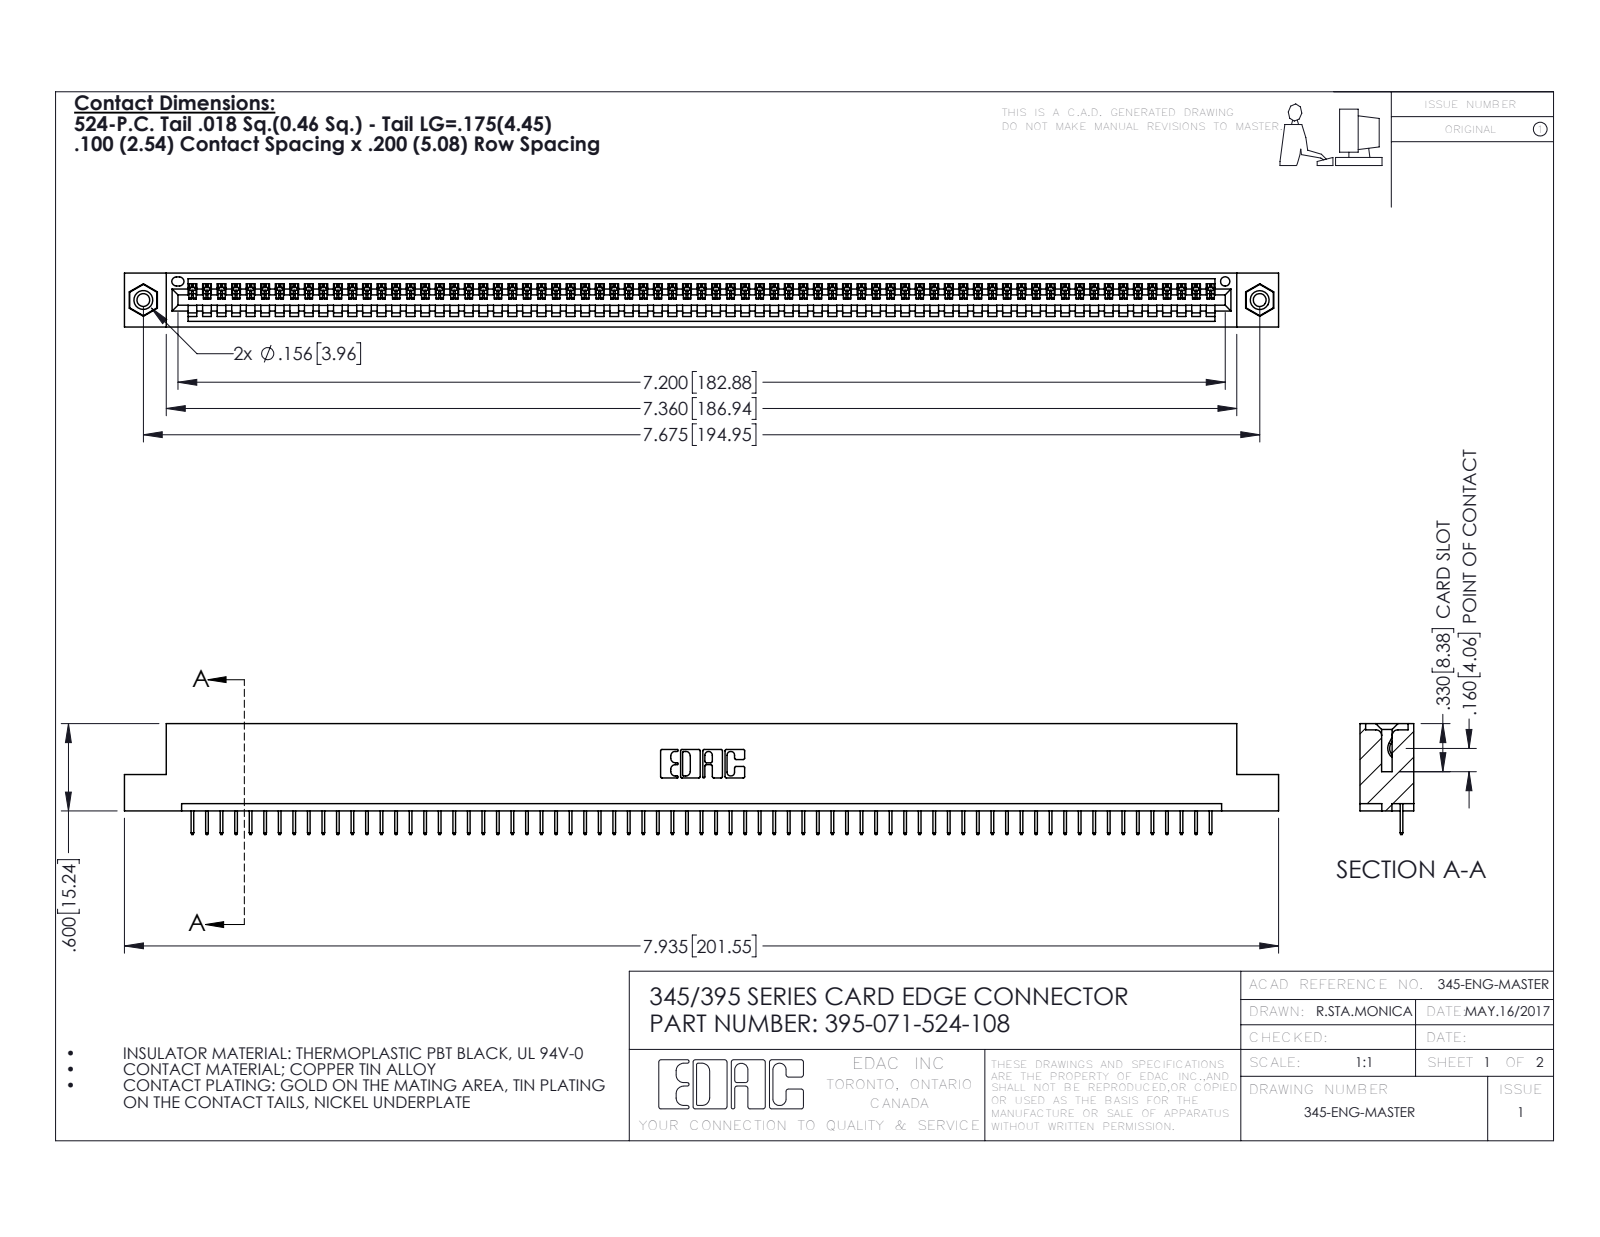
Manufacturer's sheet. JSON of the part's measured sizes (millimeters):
{"part_name": "345 Part_Flush Mounting Lugs - 0.156 Dia-TI; 345-250-001_345-250-003-102; 395-071-524-108; 345-292-001_345-293-124", "step_written_by": "SolidWorks 2016 (CONFIG_CONTROL_DESIGN)", "units": "millimeters", "bodies": {"solids": 74, "faces": 4588, "planar": 3378, "cylindrical": 1194, "other": 16}, "overall_size": [201.5, 19.4, 9.4], "volume_mm3": 19090, "surface_area_mm2": 24890, "round_holes": [[2.3, 2], [3.2, 2], [4, 2], [1.6, 1]], "round_bosses_or_shafts": [[3.9, 2]], "partial_cylinders_radius": [[0.2, 142], [0.3, 22], [0.2, 6], [0.8, 6], [0.7, 3], [0.8, 2], [1, 2], [0.4, 1]], "face_to_face_distances": [1.8, 7.6, 9.4, 5.1, 2.5, 6.9, 0.6, 5.7, 1.8, 3.8], "hole_center_spacings": [6.9, 189, 194.9]}
